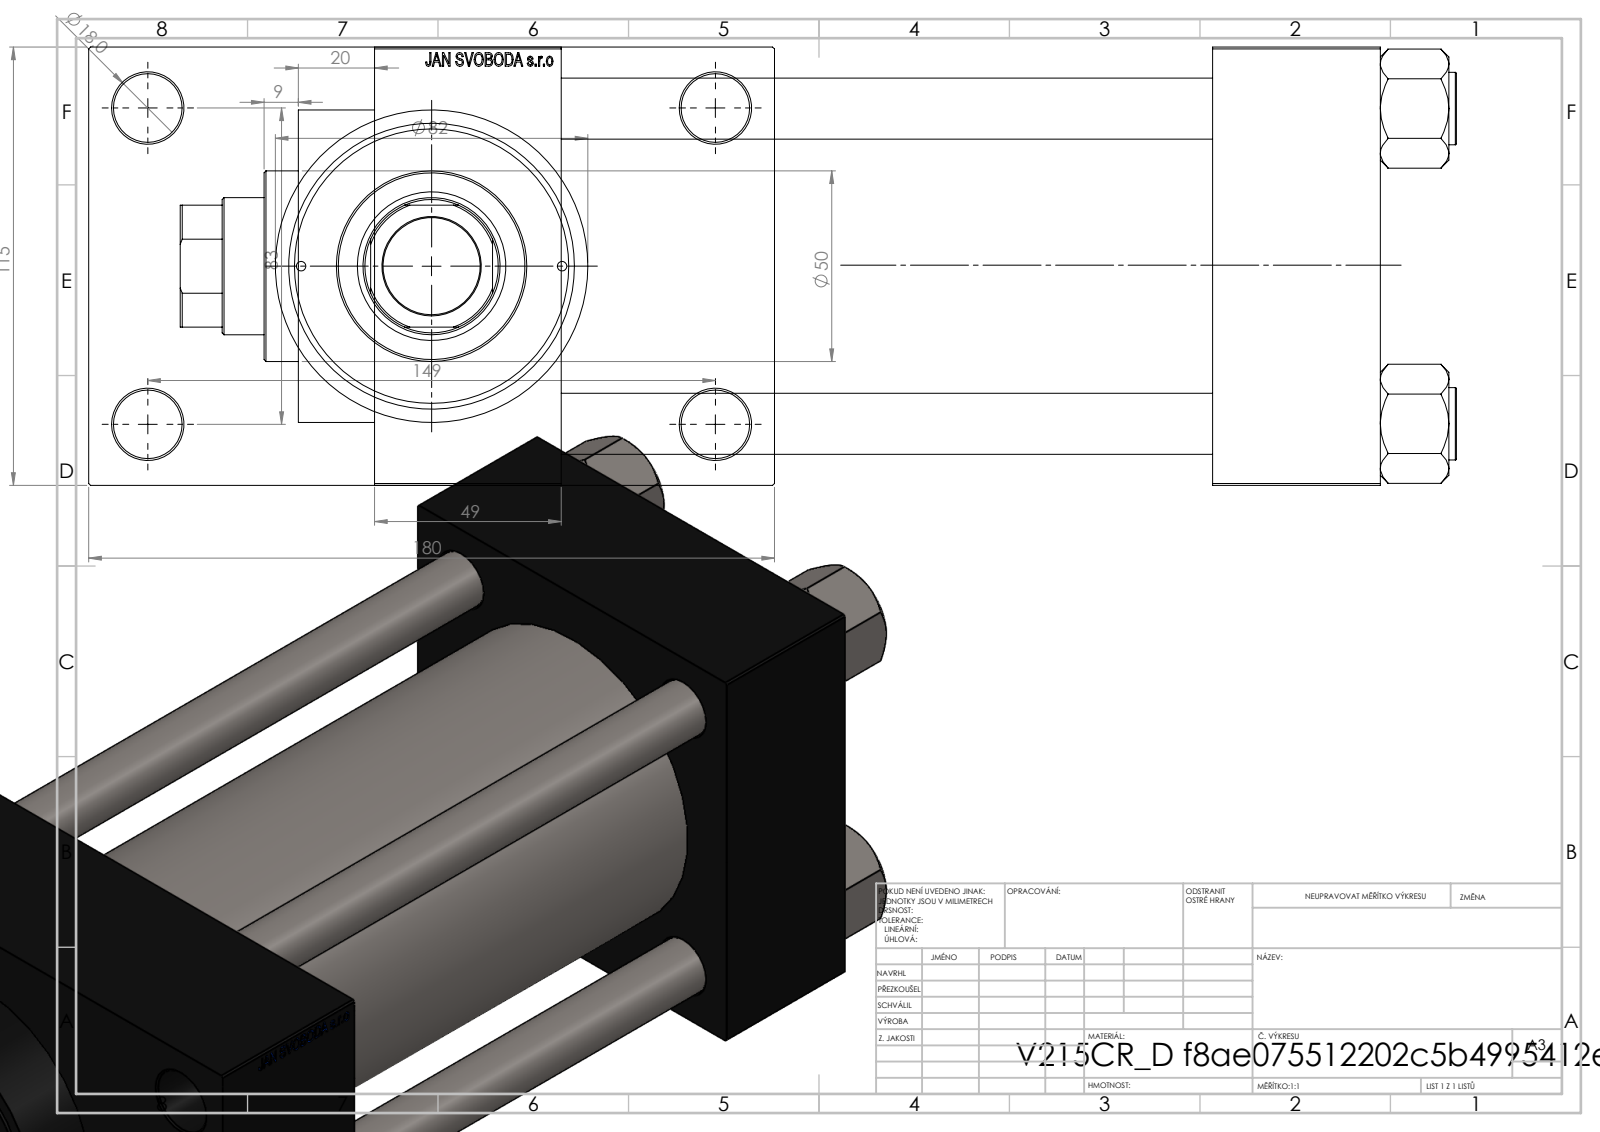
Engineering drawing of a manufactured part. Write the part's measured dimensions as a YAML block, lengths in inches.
part_name: "V215_VC_A; NUT_M5_D; V215CR_D_TYCINKA; V215CR_VCP_D (+1 more)"
step_written_by: "SolidWorks 2019 (CONFIG_CONTROL_DESIGN)"
units: inches
bodies: {solids: 11, faces: 1159, planar: 547, cylindrical: 92, other: 520}
overall_size: [13.189, 7.087, 4.528]
volume: 137.5
surface_area: 595.5
round_holes:
  - {diameter: 0.63, count: 4}
  - {diameter: 0.709, count: 4}
  - {diameter: 0.098, count: 2}
  - {diameter: 0.276, count: 2}
  - {diameter: 1.041, count: 2}
  - {diameter: 1.378, count: 2}
  - {diameter: 1.004, count: 1}
  - {diameter: 1.417, count: 1}
  - {diameter: 1.535, count: 1}
  - {diameter: 2.402, count: 1}
  - {diameter: 2.835, count: 1}
  - {diameter: 3.15, count: 1}
round_bosses_or_shafts:
  - {diameter: 0.748, count: 4}
  - {diameter: 3.386, count: 1}
  - {diameter: 3.228, count: 1}
  - {diameter: 1.969, count: 1}
partial_cylinders:
  - {radius: 0.689, count: 1}
face_to_face_distances: [4.528, 6.732, 8.661, 1.929, 1.732, 8.465, 10.394, 1.28, 5.807, 7.087]
hole_center_spacings: [1.305, 1.652, 2.276, 2.302, 3.256, 3.357, 3.393, 3.513]
